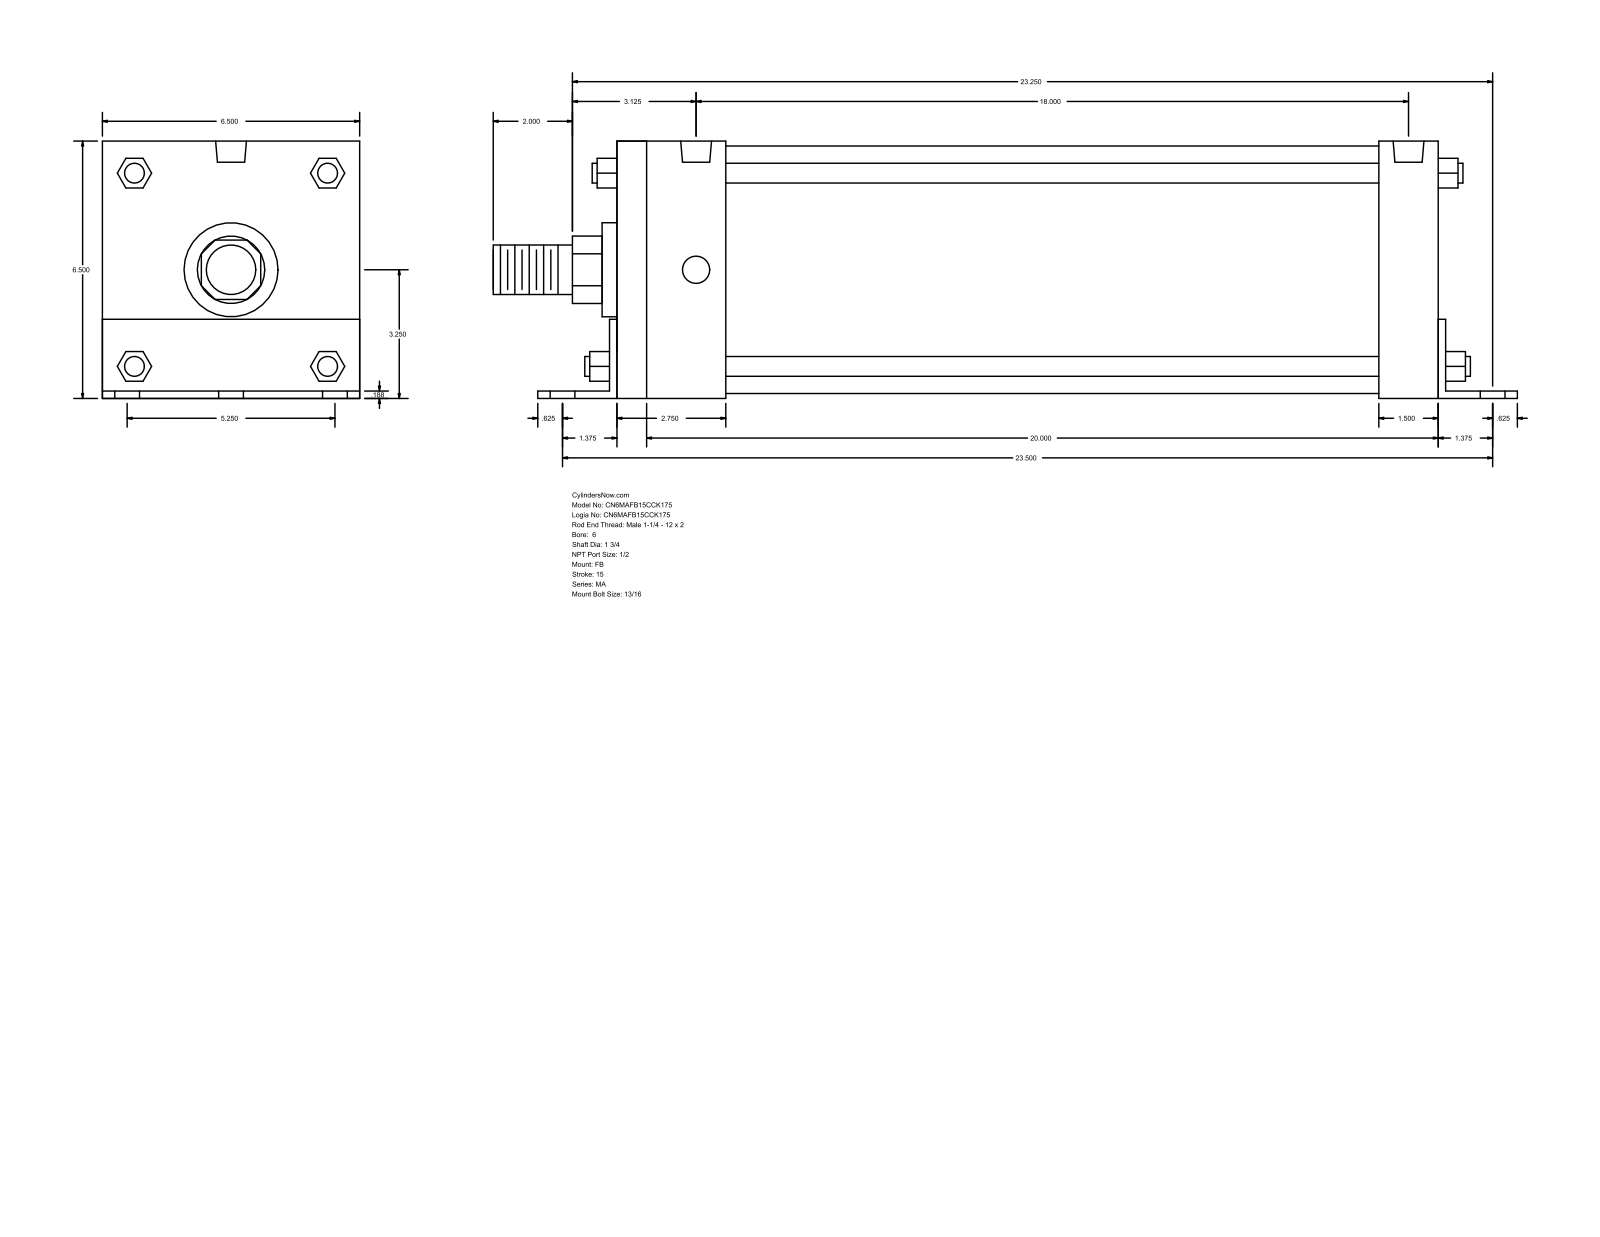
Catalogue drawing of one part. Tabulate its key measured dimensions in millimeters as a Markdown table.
| quantity | value |
| --- | --- |
| part name | MA_FB__0600_1.75 |
| STEP written by | GSSL Pune (CONFIG_CONTROL_DESIGN) |
| units | millimeters |
| bodies | 0 solids, 140 faces (105 planar, 35 cylindrical, 0 other) |
| overall size | 657.23 × 165.15 × 165.1 |
| round holes (diameter × count) | 20.64 × 6, 17.46 × 4, 19.77 × 2 |
| round bosses / shafts (diameter × count) | 12.7 × 4, 158.75 × 1, 60.33 × 1, 44.45 × 1, 31.75 × 1 |
| partial cylindrical surfaces (radius × count) | 21.63 × 1, 32.05 × 1 |
| main face-to-face distances | 165.1, 4.76, 527.05, 165.15, 4.71, 160.39, 69.85, 74.61, 38.1, 4.77 |
| hole center spacings | 66.67, 600.61, 596.9, 85.78, 108.6, 133.34, 457.2, 515.5 |
